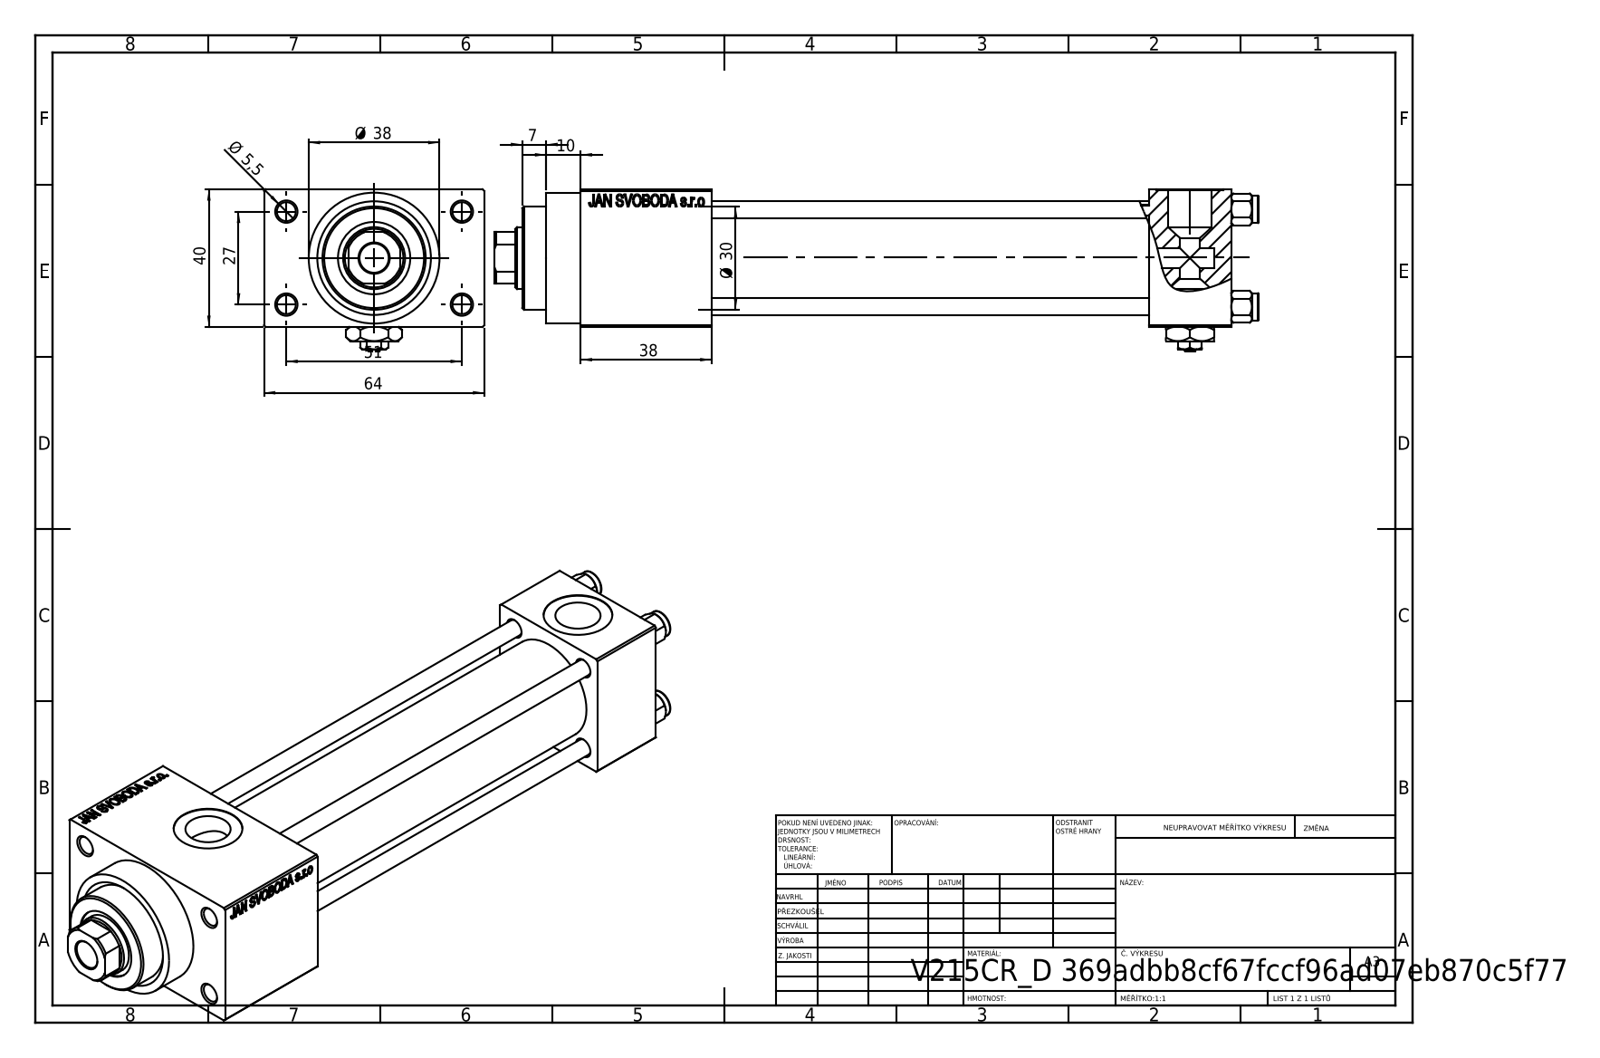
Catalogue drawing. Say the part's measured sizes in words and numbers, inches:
The part is named "Zatka_pro_OIL_PORT; V215CR_D_Body; NUT_M5_D; V215CR_D_TYCINKA (+2 more)". Its 3-D file was written by "SolidWorks 2019 (CONFIG_CONTROL_DESIGN)". It is 12 solids with 1154 faces: 518 planar, 94 cylindrical and 542 other. Overall it measures 8.74 by 2.52 by 1.85 inches. Its volume is 13.87 cubic inches and its surface area 137.7 square inches. Round holes: 4 of diameter 0.197, 4 of diameter 0.217, 3 of diameter 0.787, 2 of diameter 0.276, 2 of diameter 0.518, 1 of diameter 0.335, 1 of diameter 0.709, 1 of diameter 0.827, 1 of diameter 0.984, 1 of diameter 1.181. Round bosses or shafts: 4 of diameter 0.315, 1 of diameter 1.496, 1 of diameter 1.22. Partial cylindrical surfaces (rounded edges, fillets, slot ends): 1 of radius 0.335. The main face-to-face distances are 1.575, 0.472, 2.047, 5, 0.945, 5.945, 2.52, 1.496, 7.441, 6.496. The hole center spacings are 0.448, 0.788, 1.114, 1.136, 1.177, 1.561, 1.903, 1.063.
